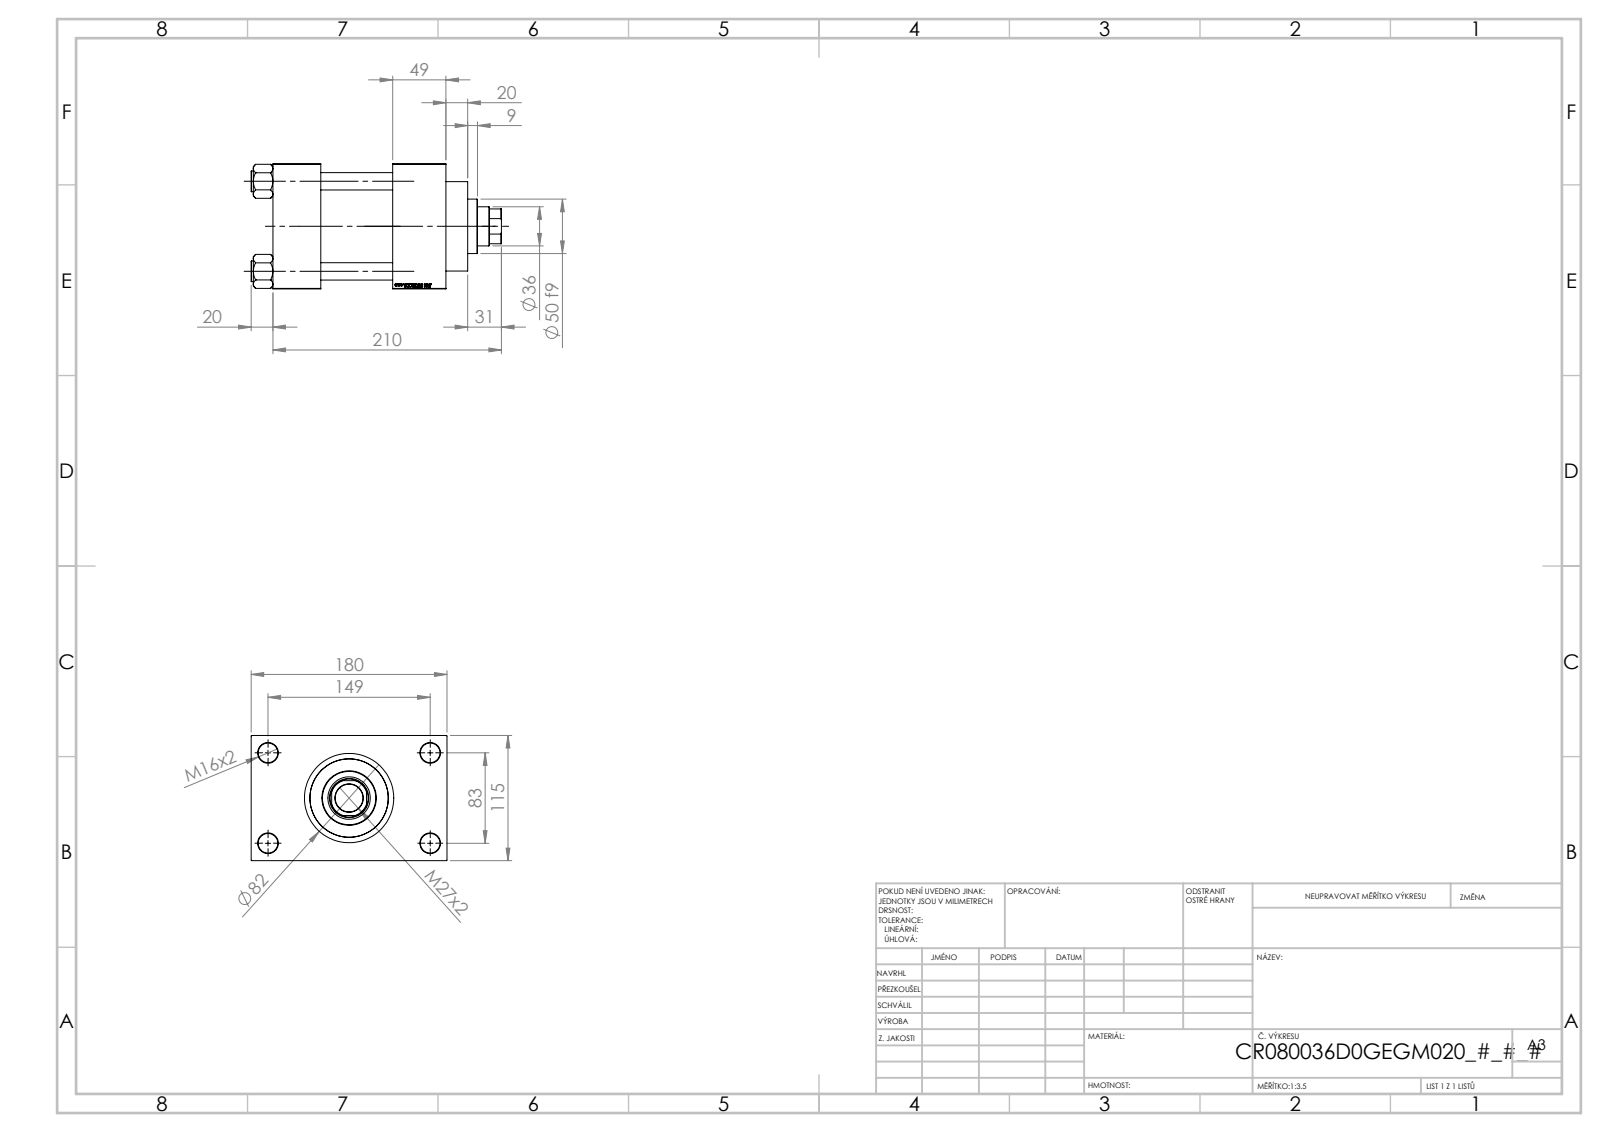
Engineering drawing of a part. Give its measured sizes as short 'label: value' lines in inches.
name: V215CR_VCP_D; V215CR_D_TYCINKA; V215_VC_A; V215CR_D_Body (+1 more)
written by: SolidWorks 2019 (CONFIG_CONTROL_DESIGN)
unit: in
bodies: 11 solids, 1152 faces (545 planar, 89 cylindrical, 518 other)
size: 9.055 × 7.087 × 4.528
volume: 121.9 in³; area: 455.5 in²
holes: 4× ⌀0.63, 4× ⌀0.709, 2× ⌀0.276, 2× ⌀1.041, 2× ⌀1.378, 1× ⌀1.004, 1× ⌀1.417, 1× ⌀1.535, 1× ⌀2.402, 1× ⌀2.835, 1× ⌀3.15
bosses: 4× ⌀0.748, 1× ⌀3.386, 1× ⌀3.228, 1× ⌀1.969
rounds: 1× R0.689
face distances: 4.528, 2.598, 4.331, 1.929, 1.732, 6.26, 1.28, 5.807, 0.787, 2.717
hole spacings: 1.305, 2.302, 3.256, 3.357, 3.513, 4.561, 5.607, 3.268
